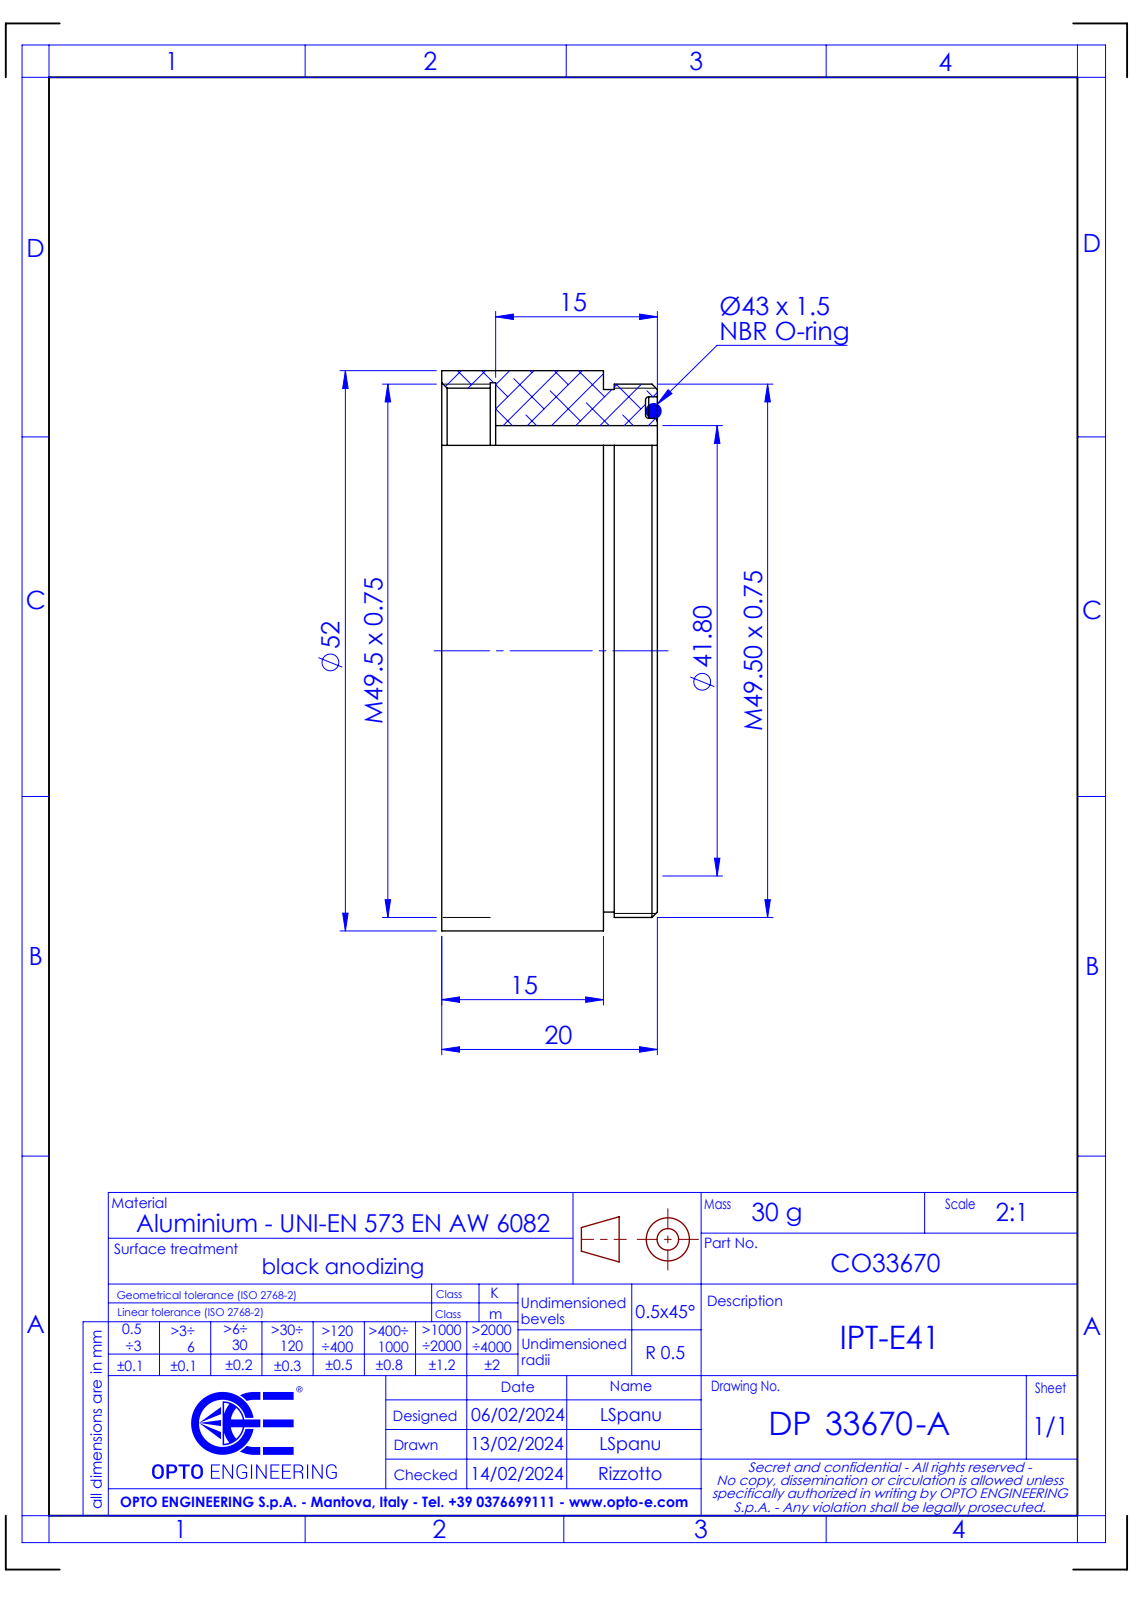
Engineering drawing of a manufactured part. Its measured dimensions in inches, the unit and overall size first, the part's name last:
Units: inches
Overall size (bounding box): 2.047 × 2.047 × 0.787
Round holes (diameter × count): ⌀1.646 ×1, ⌀1.856 ×1, ⌀1.919 ×1, ⌀1.959 ×1
Round bosses / shafts (diameter × count): ⌀2.047 ×1, ⌀1.949 ×1, ⌀1.909 ×1, ⌀1.699 ×1
Main face-to-face distances: 0.197, 0.591, 0.394, 0.547, 0.154, 0.744, 0.787, 0.043, 0.177, 0.02
Volume: 0.677 in³ · Surface area: 12.31 in²
Bodies: 1 solid, 34 faces (8 planar, 16 cylindrical, 10 other)
Part name (STEP PRODUCT): DP33670-A_IPT-E41
STEP written by: SolidWorks 2021 (CONFIG_CONTROL_DESIGN)
